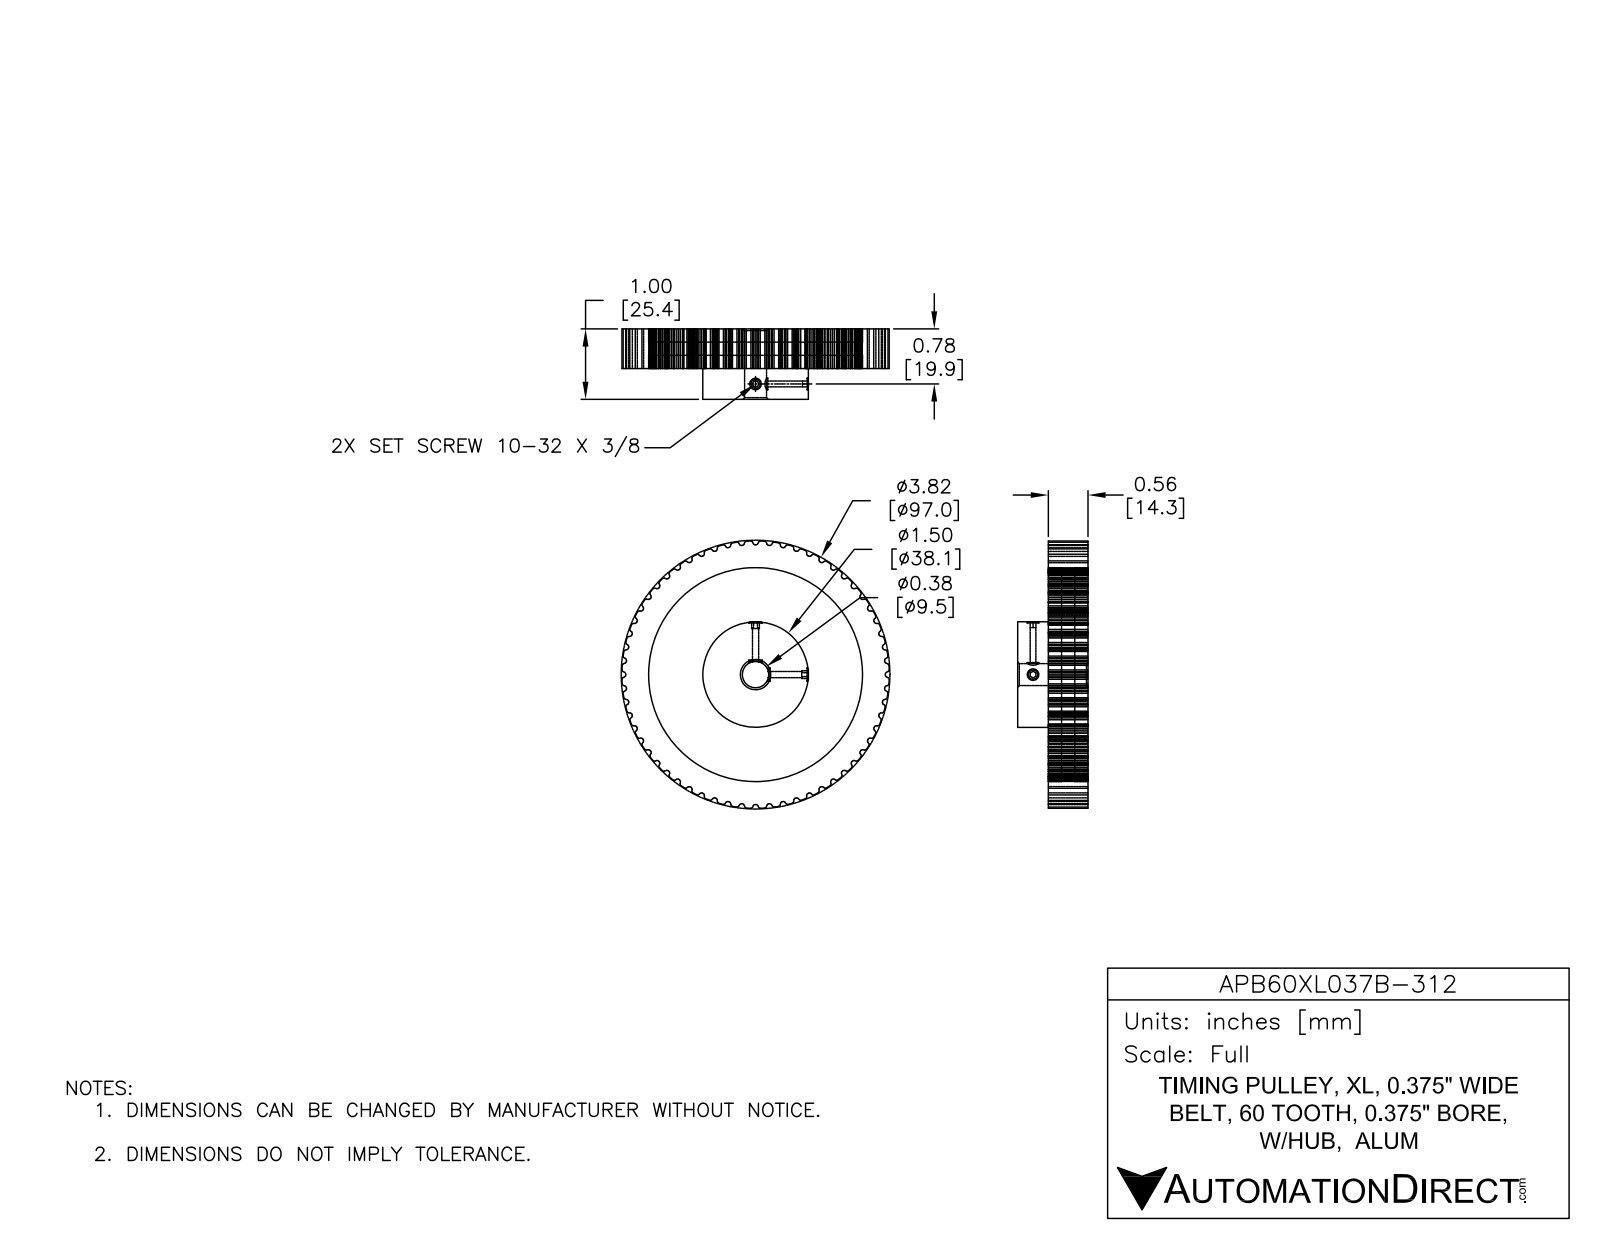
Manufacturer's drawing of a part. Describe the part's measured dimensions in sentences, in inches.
The part is named "APB60XL037B-375". Its 3-D file was written by "SolidWorks 2014 (AUTOMOTIVE_DESIGN)". It is 1 solid with 558 faces: 127 planar, 421 cylindrical and 10 other. Overall it measures 3.8 by 3.8 by 1 inches. Its volume is 5.027 cubic inches and its surface area 39.8 square inches. Round holes: 2 of diameter 0.088, 1 of diameter 0.375, 1 of diameter 3.04. Round bosses or shafts: 1 of diameter 1.5, 1 of diameter 0.93. Partial cylindrical surfaces (rounded edges, fillets, slot ends): 240 of radius 0.015, 1 of radius 1.845, 1 of radius 1.9. The main face-to-face distances are 0.28, 0.42, 0.14, 0.14, 0.42, 0.56, 1, 0.86, 0.58, 0.44.
